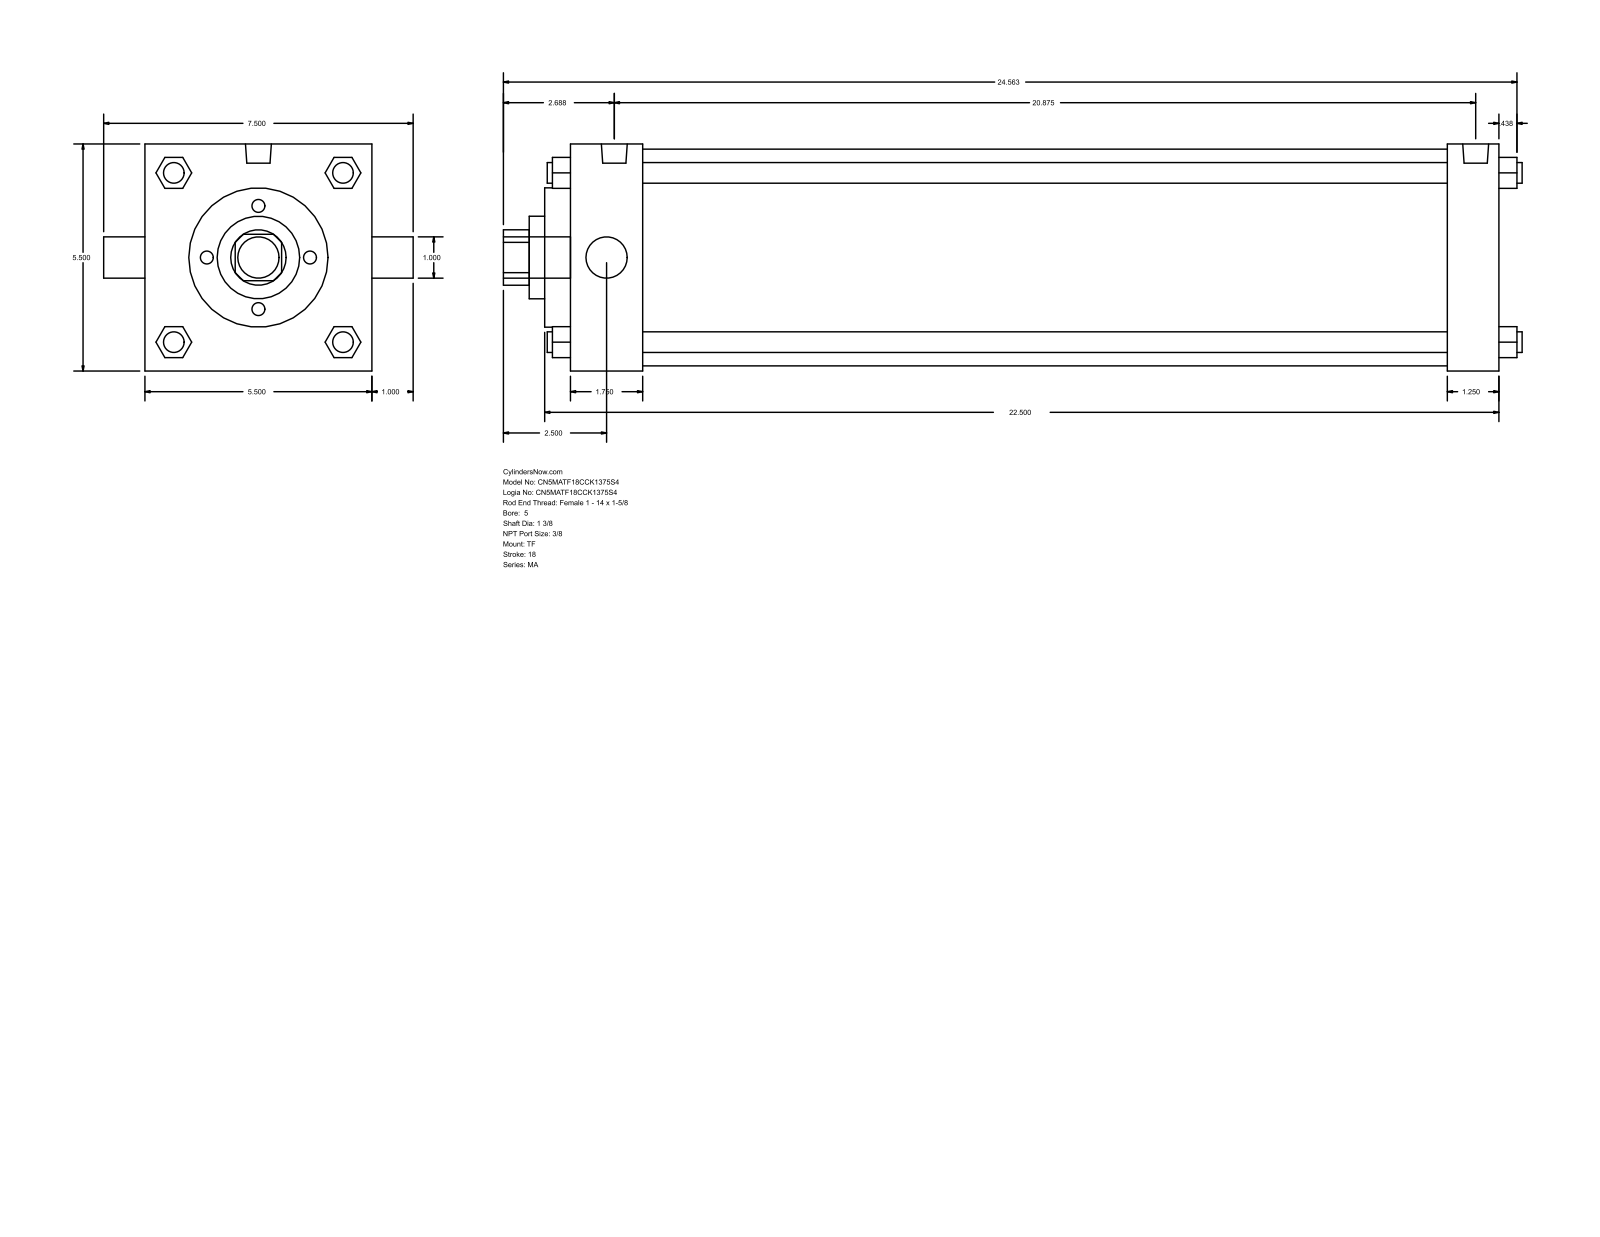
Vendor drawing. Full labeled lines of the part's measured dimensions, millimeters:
Part name (STEP PRODUCT): MA_TF__0500_1.375
STEP written by: GSSL Pune (CONFIG_CONTROL_DESIGN)
Units: millimetres
Bodies: 0 solids, 122 faces (93 planar, 29 cylindrical, 0 other)
Overall size (bounding box): 627.06 × 190.5 × 139.7
Round holes (diameter × count): ⌀25.4 ×1, ⌀34.92 ×1, ⌀50.8 ×1, ⌀85.72 ×1, ⌀133.35 ×1
Round bosses / shafts (diameter × count): ⌀12.7 ×4, ⌀11.11 ×3, ⌀15.93 ×2, ⌀25.4 ×1
Partial cylindrical surfaces — rounded edges, fillets, slot ends (radius × count): R17.06 ×1
Main face-to-face distances: 139.7, 571.5, 539.75, 31.75, 44.45, 495.3, 527.05, 15.87, 60.32, 555.62
